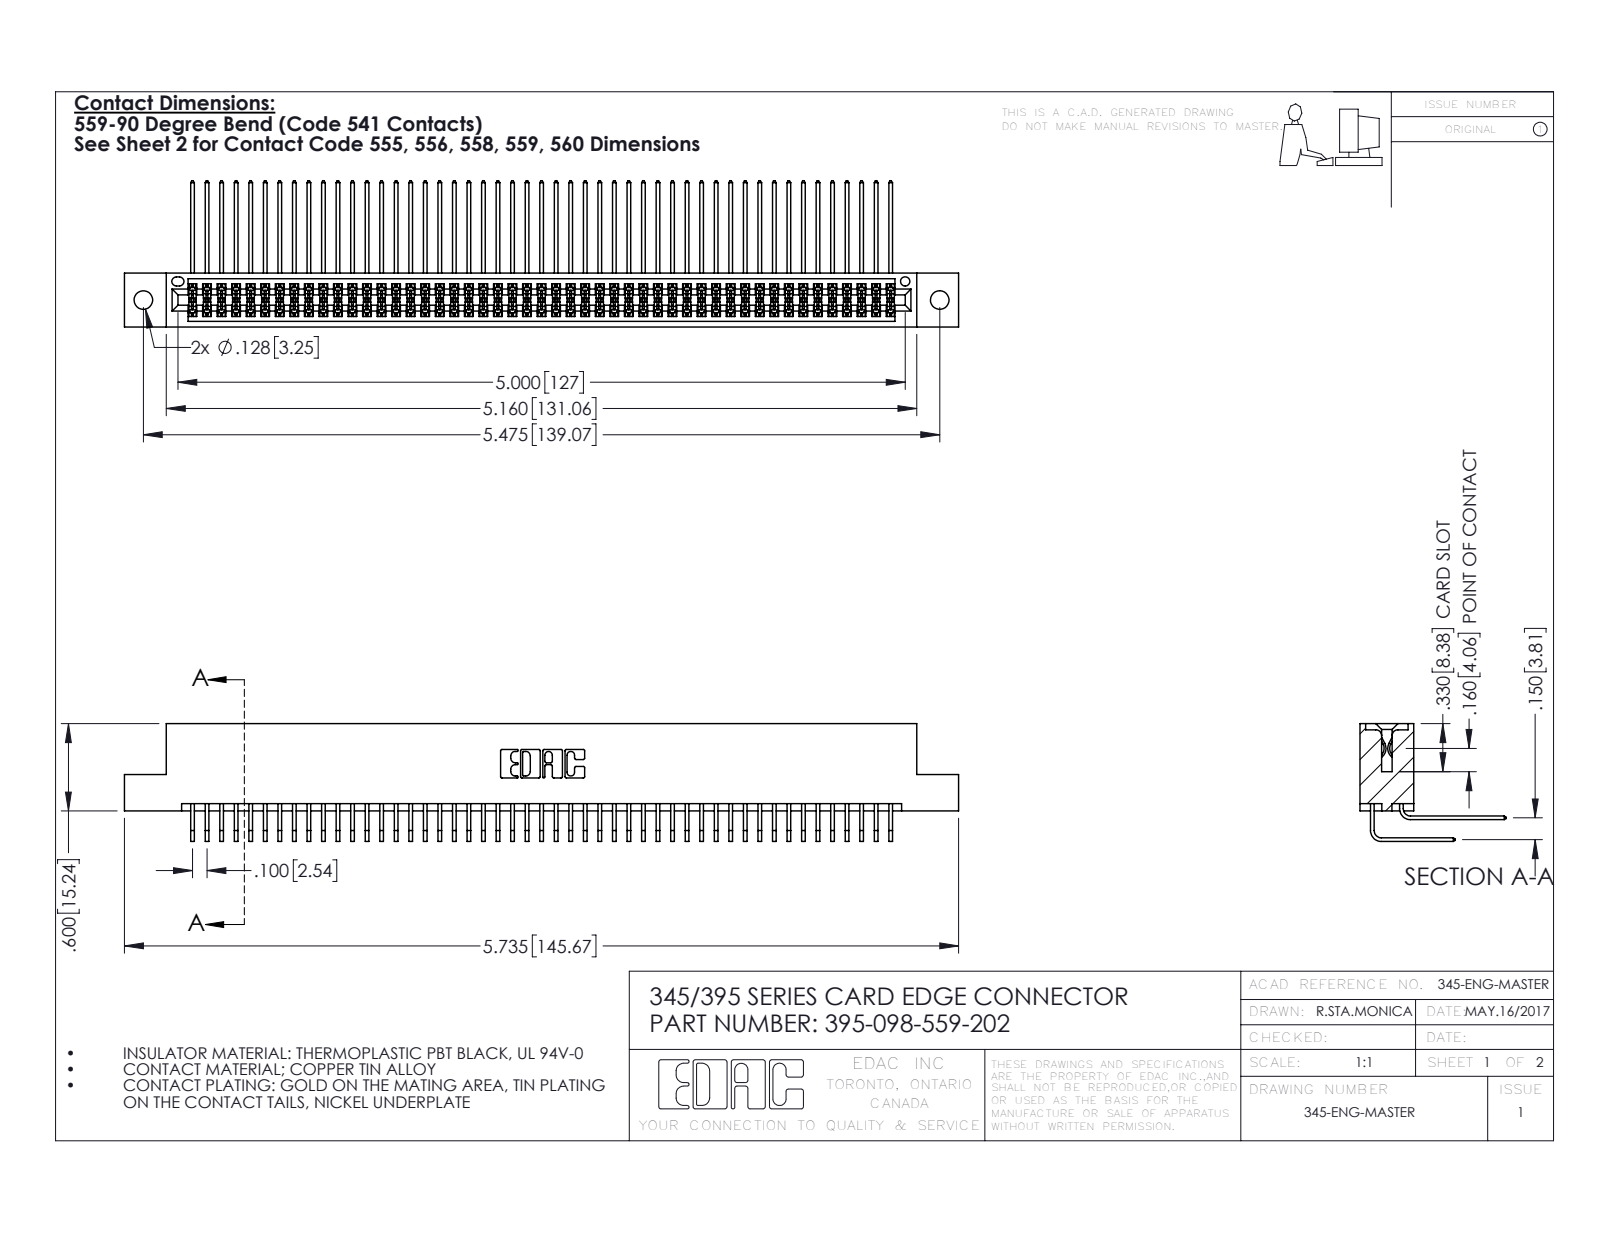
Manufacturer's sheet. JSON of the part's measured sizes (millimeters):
{"part_name": "395-098-559-202; 345-292-001_558 559 Tail - 1; 345 Part_Flush Mounting Lugs - 0.128 Dia; 345-292-001_559 Tail - 2", "step_written_by": "SolidWorks 2016 (CONFIG_CONTROL_DESIGN)", "units": "millimeters", "bodies": {"solids": 99, "faces": 5222, "planar": 3510, "cylindrical": 1712, "other": 0}, "overall_size": [145.7, 25.5, 20.5], "volume_mm3": 14700, "surface_area_mm2": 24320, "round_holes": [[3.3, 2], [1.6, 1]], "partial_cylinders_radius": [[0.2, 148], [0.3, 22], [0.2, 6], [0.8, 6], [0.7, 3], [0.4, 2], [0.5, 2], [0.6, 2]], "face_to_face_distances": [1.8, 7.6, 5.1, 9.4, 2.5, 6.9, 0.6, 5.7, 4.4, 3.8], "hole_center_spacings": [6.9, 133.1, 139.1]}
